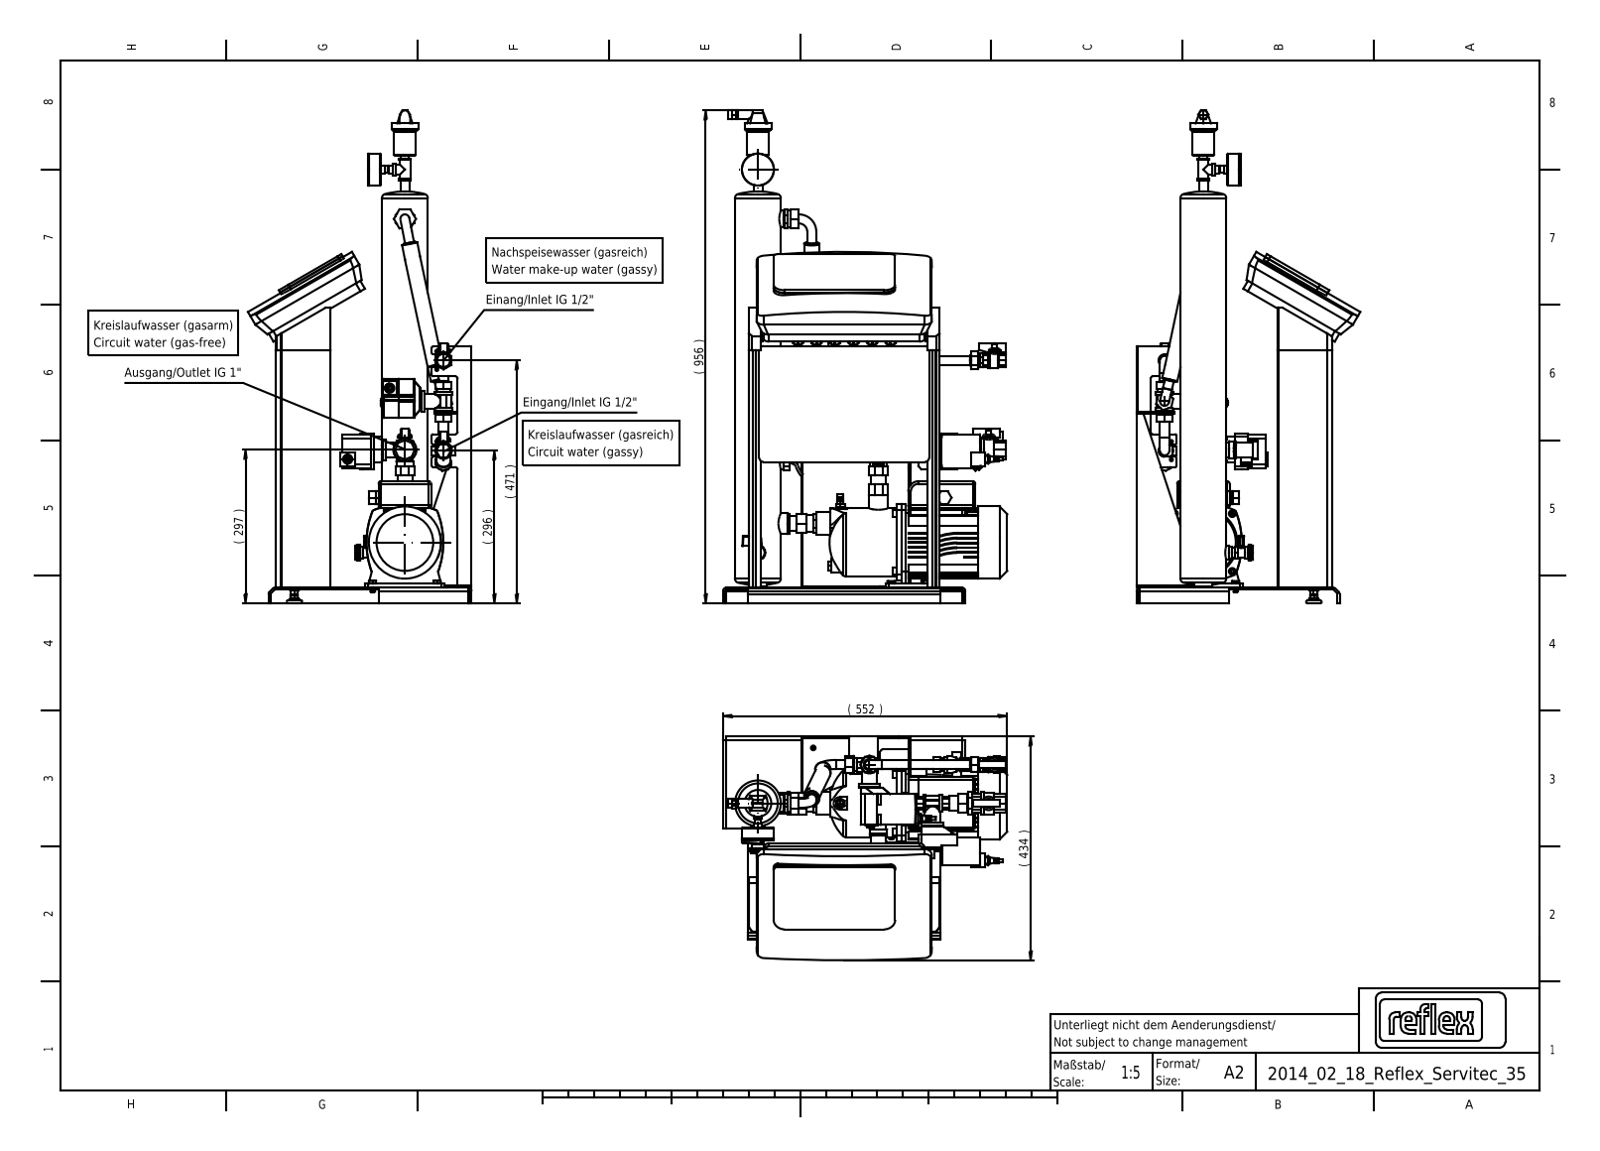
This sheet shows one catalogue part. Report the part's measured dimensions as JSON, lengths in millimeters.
{"step_written_by": "Mechanical Desktop 2011 (CONFIG_CONTROL_DESIGN)", "units": "millimeters", "bodies": {"solids": 72, "faces": 2768, "planar": 1477, "cylindrical": 740, "other": 551}, "overall_size": [956.09, 551.5, 434], "volume_mm3": 21790000, "surface_area_mm2": 2403000, "round_holes": [[6.1, 8], [9, 7], [10.5, 7], [17, 7], [6, 4], [5, 2], [8.4, 2], [23, 2], [1, 1], [6.2, 1], [13, 1], [15, 1]], "round_bosses_or_shafts": [[16, 13], [30, 8], [18, 8], [17.5, 8], [19, 7], [8, 7], [28, 5], [26, 5]], "partial_cylinders_radius": [[0.5, 56], [5, 28], [1, 26], [1.33, 16], [3, 14], [105, 10], [10, 6], [2.5, 5]], "face_to_face_distances": [4, 366, 3, 73.51, 191.5, 272.51, 346.02, 194.5, 81, 205], "hole_center_spacings": [36, 27, 72, 108, 29, 35, 39.51, 39.62]}
